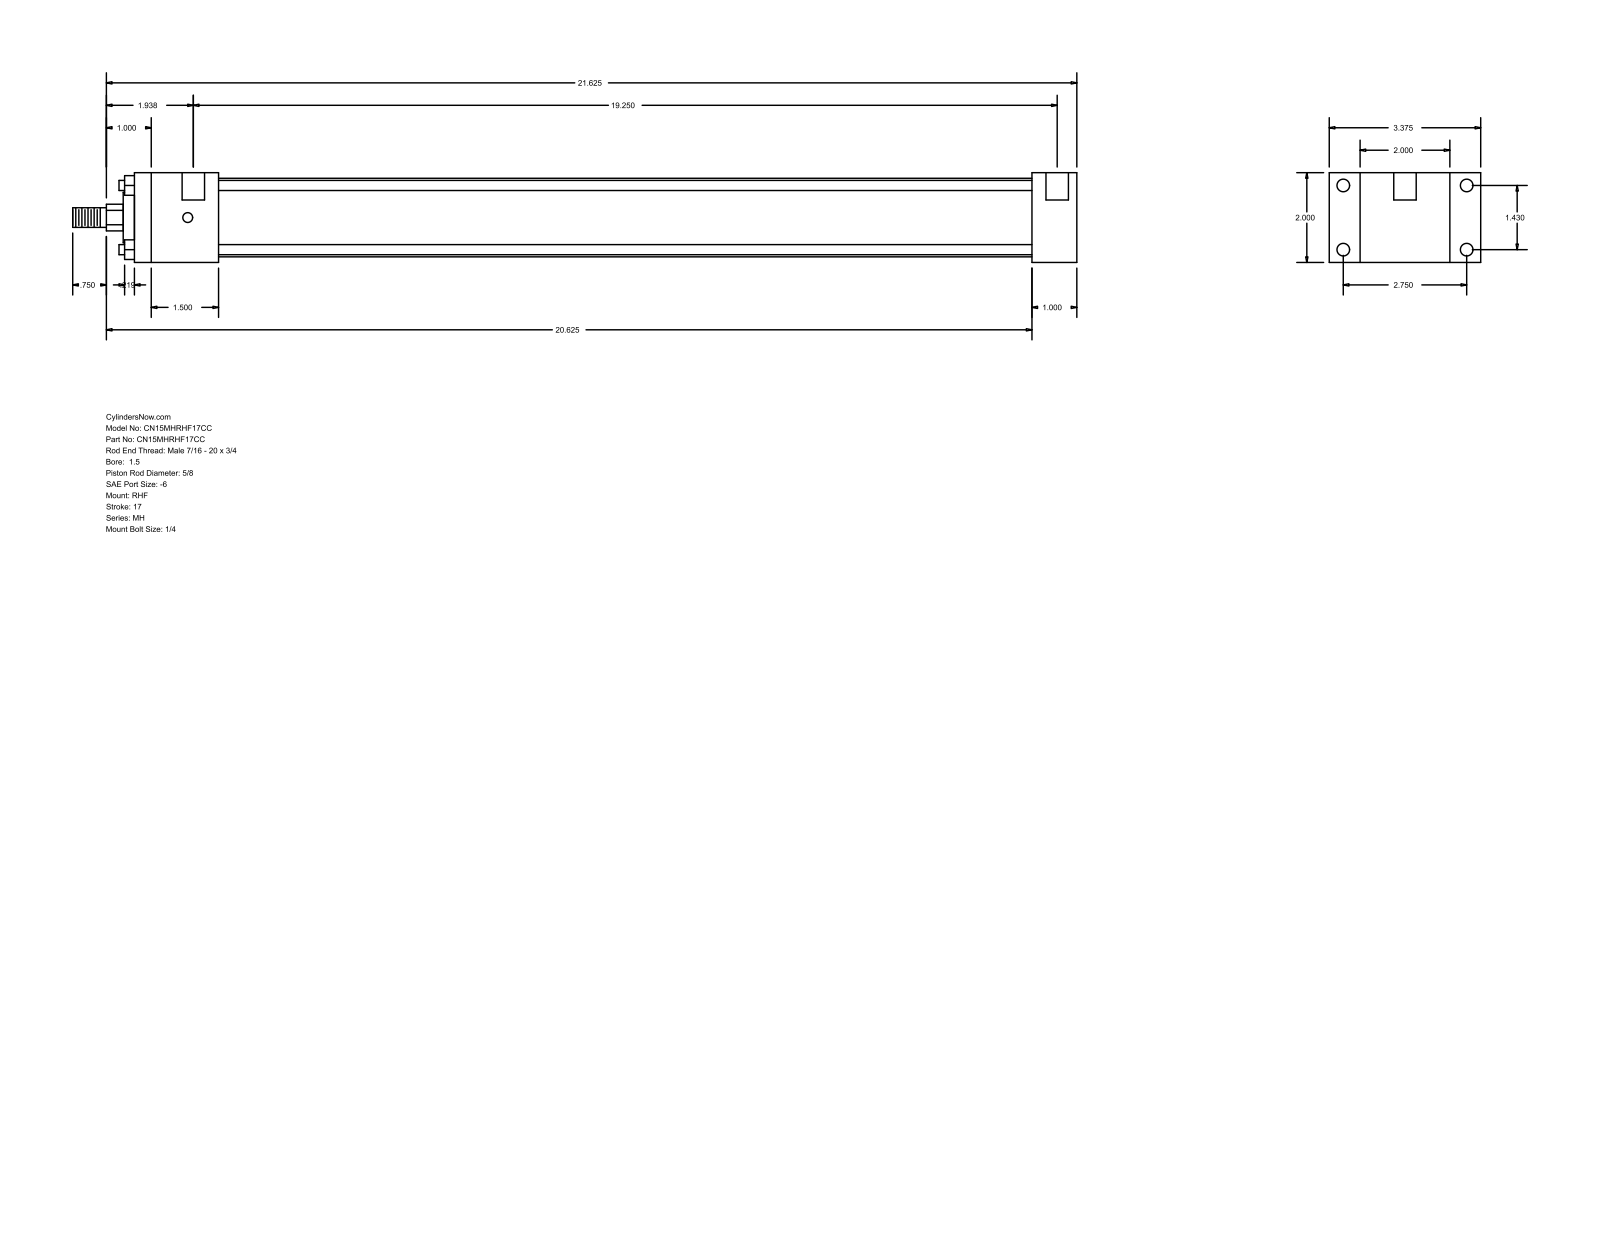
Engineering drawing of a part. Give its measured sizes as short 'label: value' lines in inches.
name: MH_RHF__0150_0.625
written by: GSSL Pune (CONFIG_CONTROL_DESIGN)
unit: in
bodies: 0 solids, 88 faces (60 planar, 28 cylindrical, 0 other)
size: 22.375 × 3.375 × 2
holes: 4× ⌀0.219, 4× ⌀0.281, 2× ⌀0.5
bosses: 4× ⌀0.225, 1× ⌀1.75, 1× ⌀1.125, 1× ⌀0.625, 1× ⌀0.437
rounds: 1× R0.297
face distances: 2, 0.687, 2.687, 1, 20, 21, 3.375, 1.875, 18.125, 19.125
hole spacings: 1.43, 2.75, 3.099, 19.375, 0.125, 19.25
